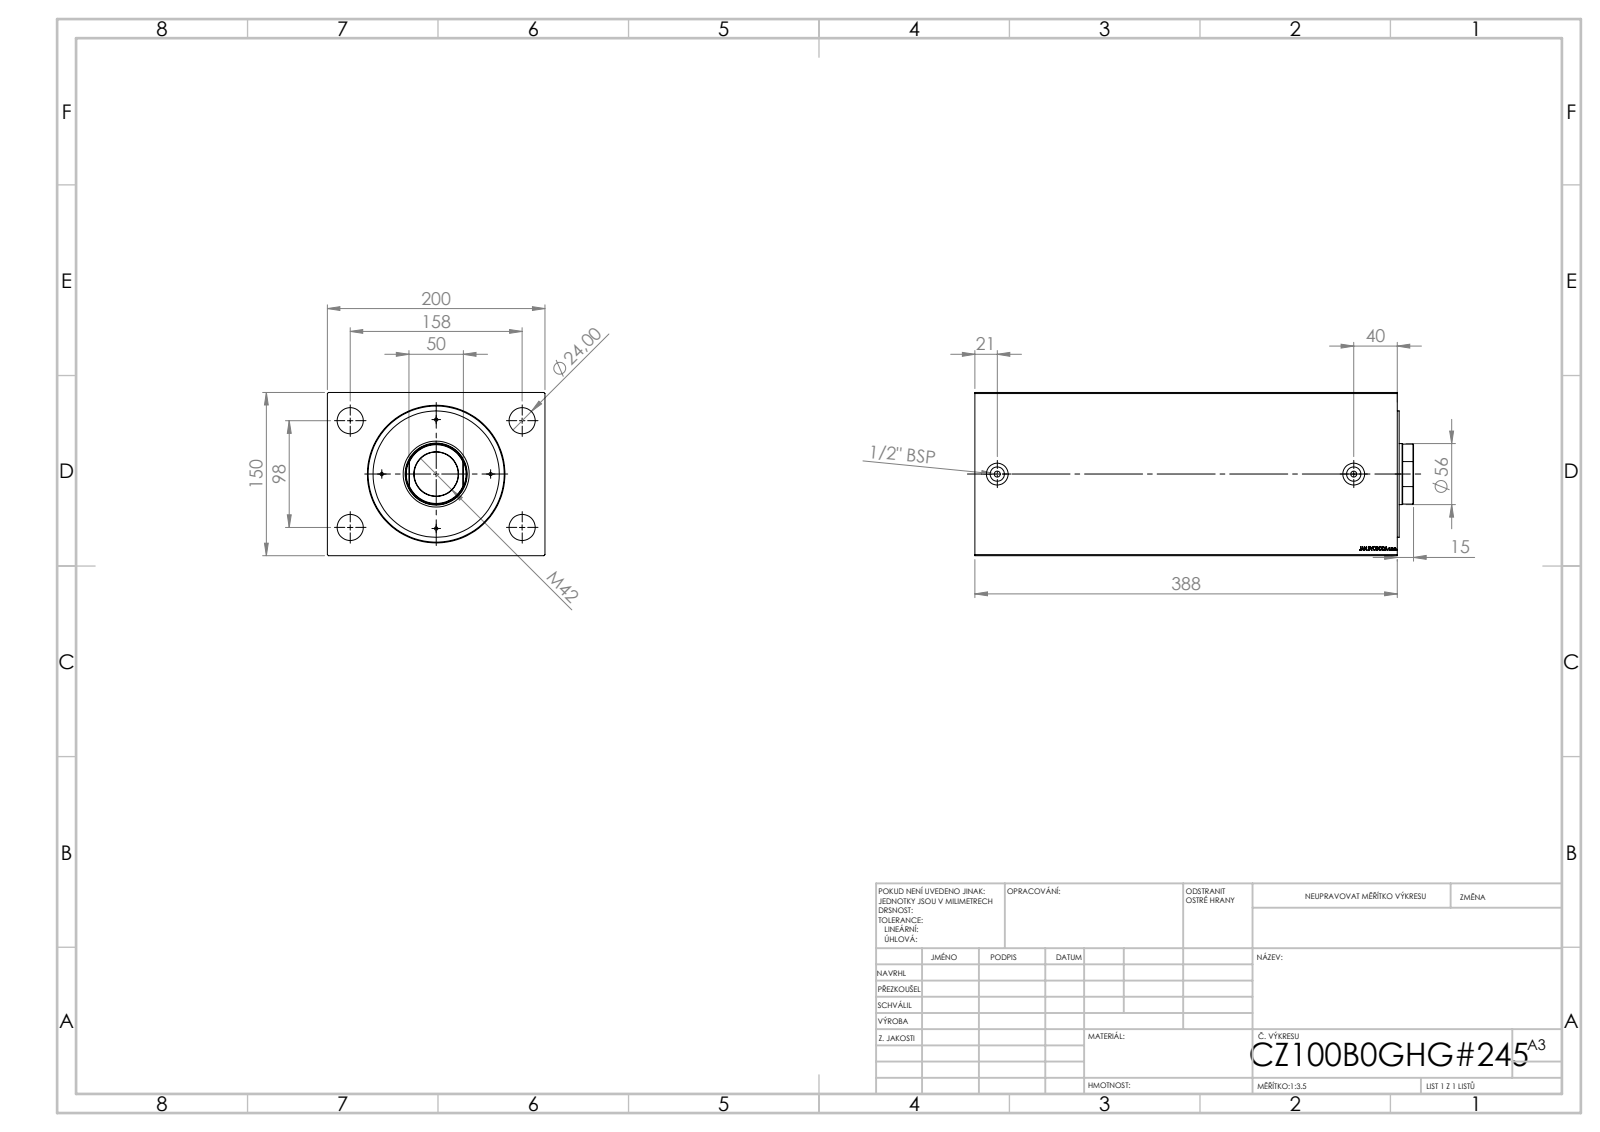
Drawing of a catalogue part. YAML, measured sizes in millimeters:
part_name: "V500CZ; V500CZ_B_VC"
step_written_by: "SolidWorks 2019 (CONFIG_CONTROL_DESIGN)"
units: millimeters
bodies: {solids: 3, faces: 874, planar: 400, cylindrical: 58, other: 416}
overall_size: [403, 200, 150]
volume: 10160000
surface_area: 589834
round_holes:
  - {diameter: 3, count: 4}
  - {diameter: 24, count: 4}
  - {diameter: 5.5, count: 2}
  - {diameter: 13.16, count: 2}
  - {diameter: 20, count: 2}
  - {diameter: 36, count: 1}
  - {diameter: 40.5, count: 1}
  - {diameter: 56, count: 1}
  - {diameter: 57, count: 1}
  - {diameter: 100, count: 1}
  - {diameter: 125, count: 1}
round_bosses_or_shafts:
  - {diameter: 116, count: 1}
partial_cylinders:
  - {radius: 27.5, count: 1}
face_to_face_distances: [150, 200, 388, 354.7, 33.3, 15, 1.8, 13.2, 341.5, 374.8]
hole_center_spacings: [50, 56.94, 70.71, 79.01, 92.96, 126.66, 137.99, 98]
